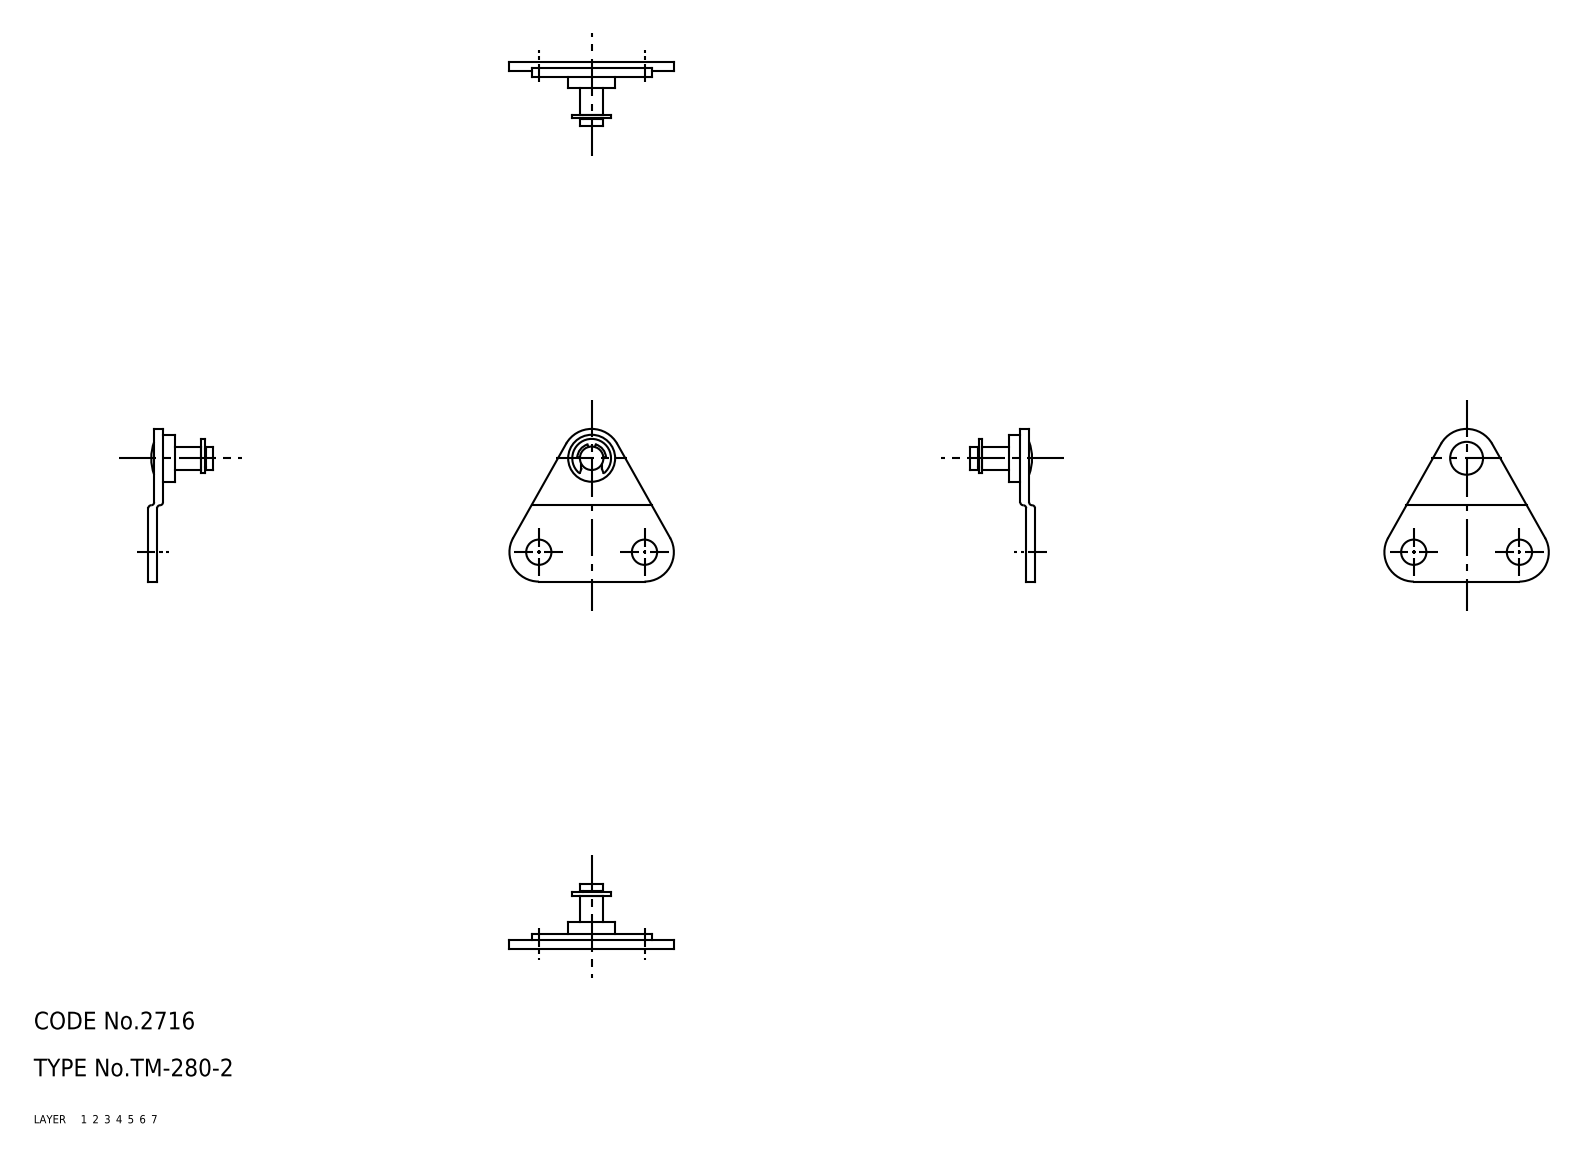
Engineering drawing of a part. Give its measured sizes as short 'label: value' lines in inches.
name: retainer; bracket; TM_280_2_30720_36
written by: CADfix (AUTOMOTIVE_DESIGN)
unit: in
bodies: 2 solids, 56 faces (0 planar, 0 cylindrical, 56 other)
size: 1.102 × 1.024 × 0.433
volume: 0.055 in³; area: 2.04 in²
